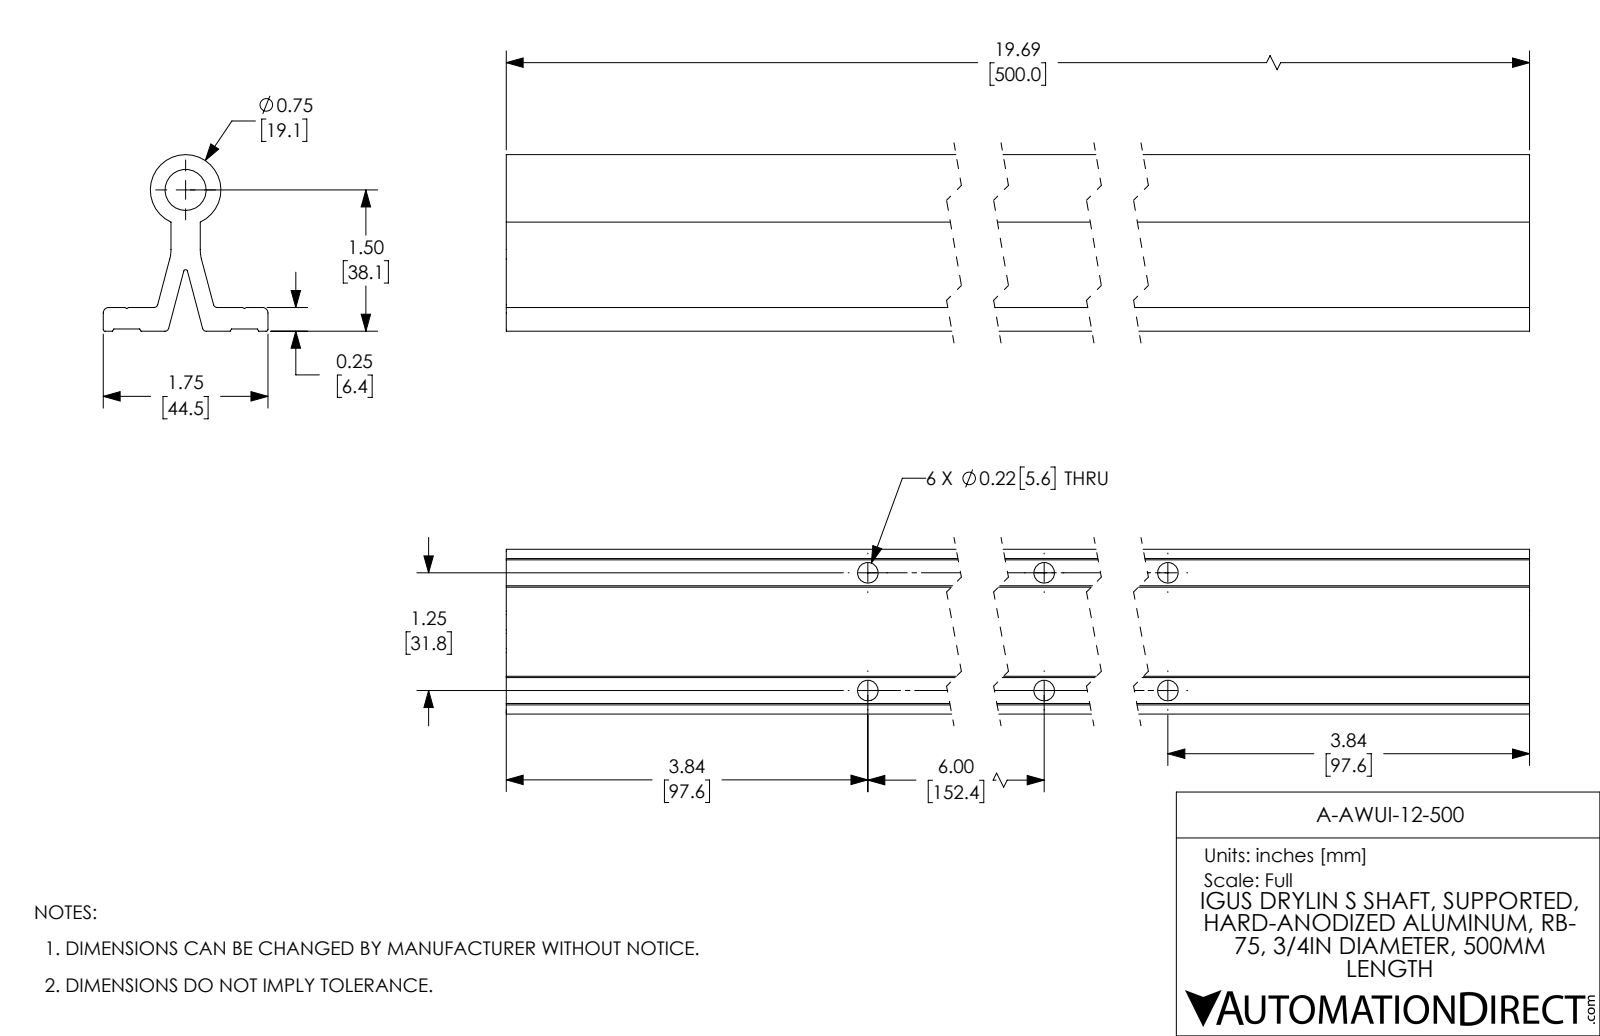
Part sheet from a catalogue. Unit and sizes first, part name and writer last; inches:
Units: inches
Overall size (bounding box): 19.685 × 1.875 × 1.75
Round holes (diameter × count): ⌀0.22 ×6, ⌀0.437 ×1
Round bosses / shafts (diameter × count): ⌀0.75 ×1
Partial cylindrical surfaces — rounded edges, fillets, slot ends (radius × count): R0.039 ×4, R0.02 ×3, R0.059 ×2, R0.394 ×2
Main face-to-face distances: 0.177, 0.252, 0.024, 0.228, 0.311, 0.72, 1.031, 1.75, 1.03, 0.719
Hole centre spacings: 6, 6.129, 1.25, 12, 12.065
Volume: 18.52 in³ · Surface area: 191.6 in²
Bodies: 1 solid, 66 faces (40 planar, 26 cylindrical, 0 other)
Part name (STEP PRODUCT): A-AWUI-12-500
STEP written by: SolidWorks 2017 (AUTOMOTIVE_DESIGN)
